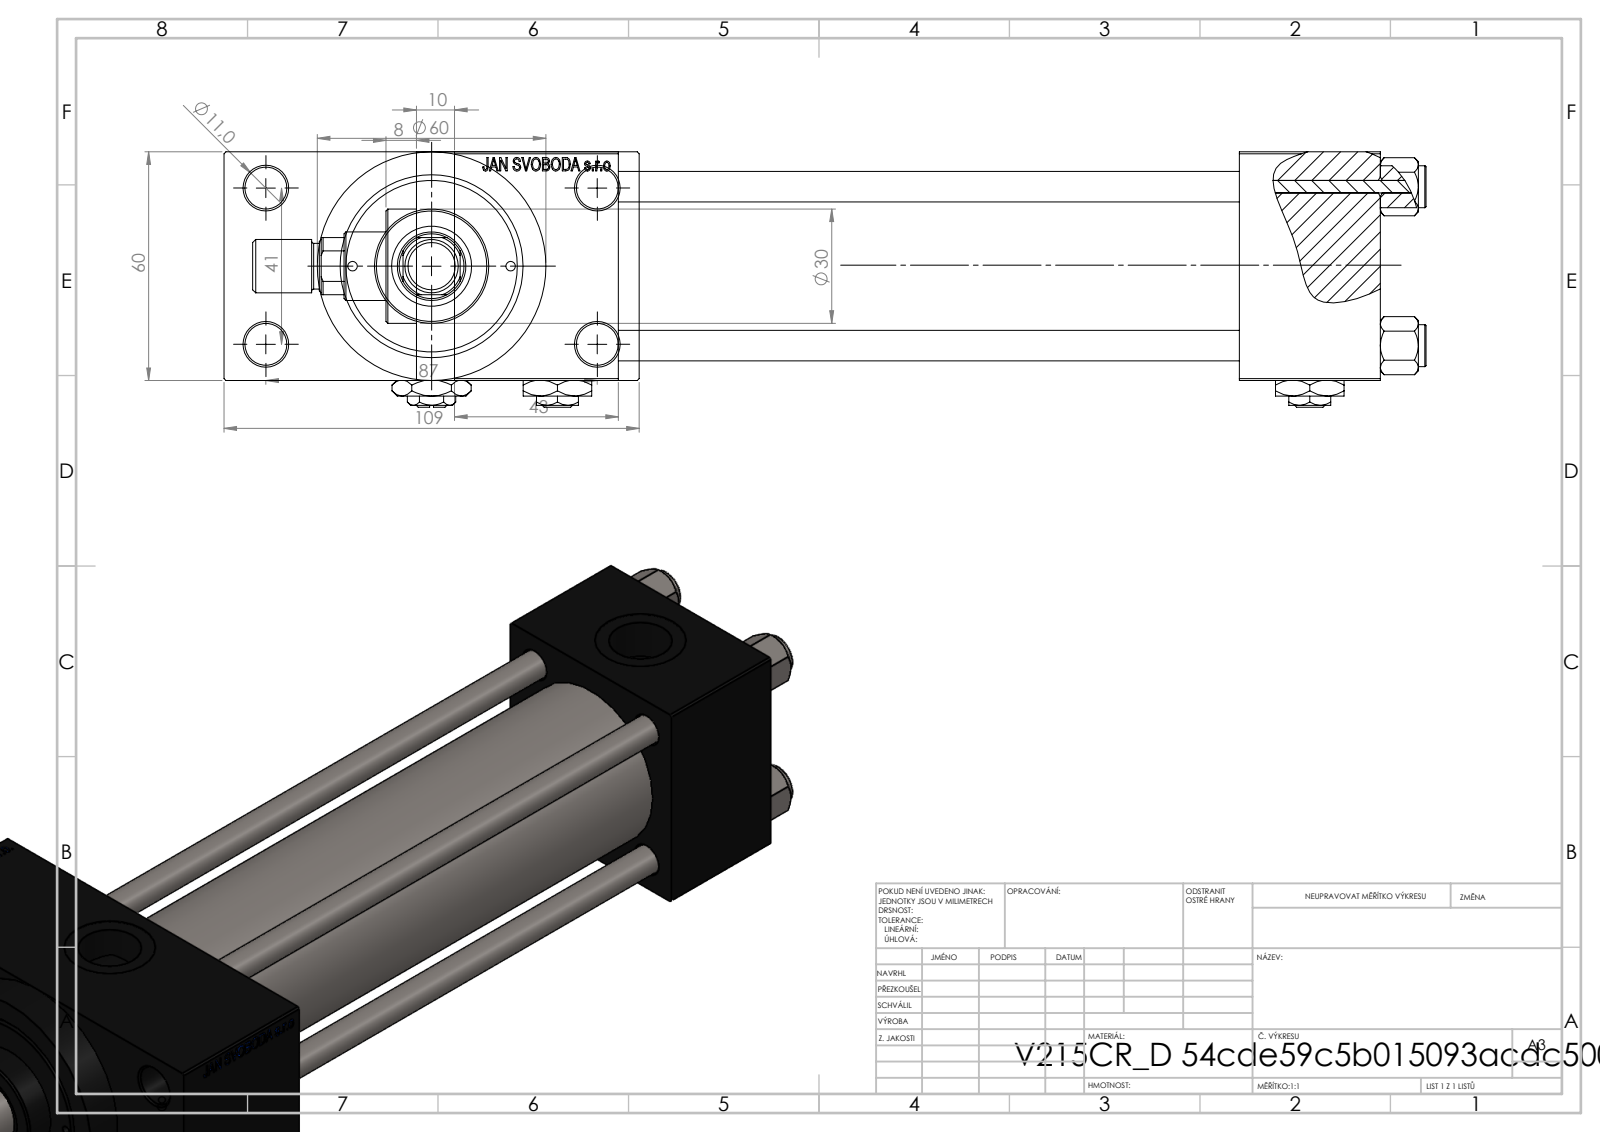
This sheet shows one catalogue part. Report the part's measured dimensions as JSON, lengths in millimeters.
{"part_name": "Zatka_pro_OIL_PORT; NUT_M5_D; V215CR_VCP_D; V215CR_D_Body (+3 more)", "step_written_by": "SolidWorks 2019 (CONFIG_CONTROL_DESIGN)", "units": "millimeters", "bodies": {"solids": 14, "faces": 1228, "planar": 552, "cylindrical": 108, "other": 568}, "overall_size": [308, 109, 67], "volume_mm3": 608436, "surface_area_mm2": 169860, "round_holes": [[8, 4], [11, 4], [2.5, 2], [7, 2], [16.66, 2], [24, 2], [8.5, 1], [18, 1], [21, 1], [31, 1], [40, 1], [45, 1]], "round_bosses_or_shafts": [[11, 4], [60, 1], [46, 1], [30, 1], [14, 1], [12, 1]], "partial_cylinders_radius": [[8.5, 1]], "face_to_face_distances": [60, 24.5, 84.5, 163, 37, 200, 43, 243, 206, 109], "hole_center_spacings": [20.85, 22.65, 29.49, 30.62, 41.7, 46.53, 47.15, 48.09]}
